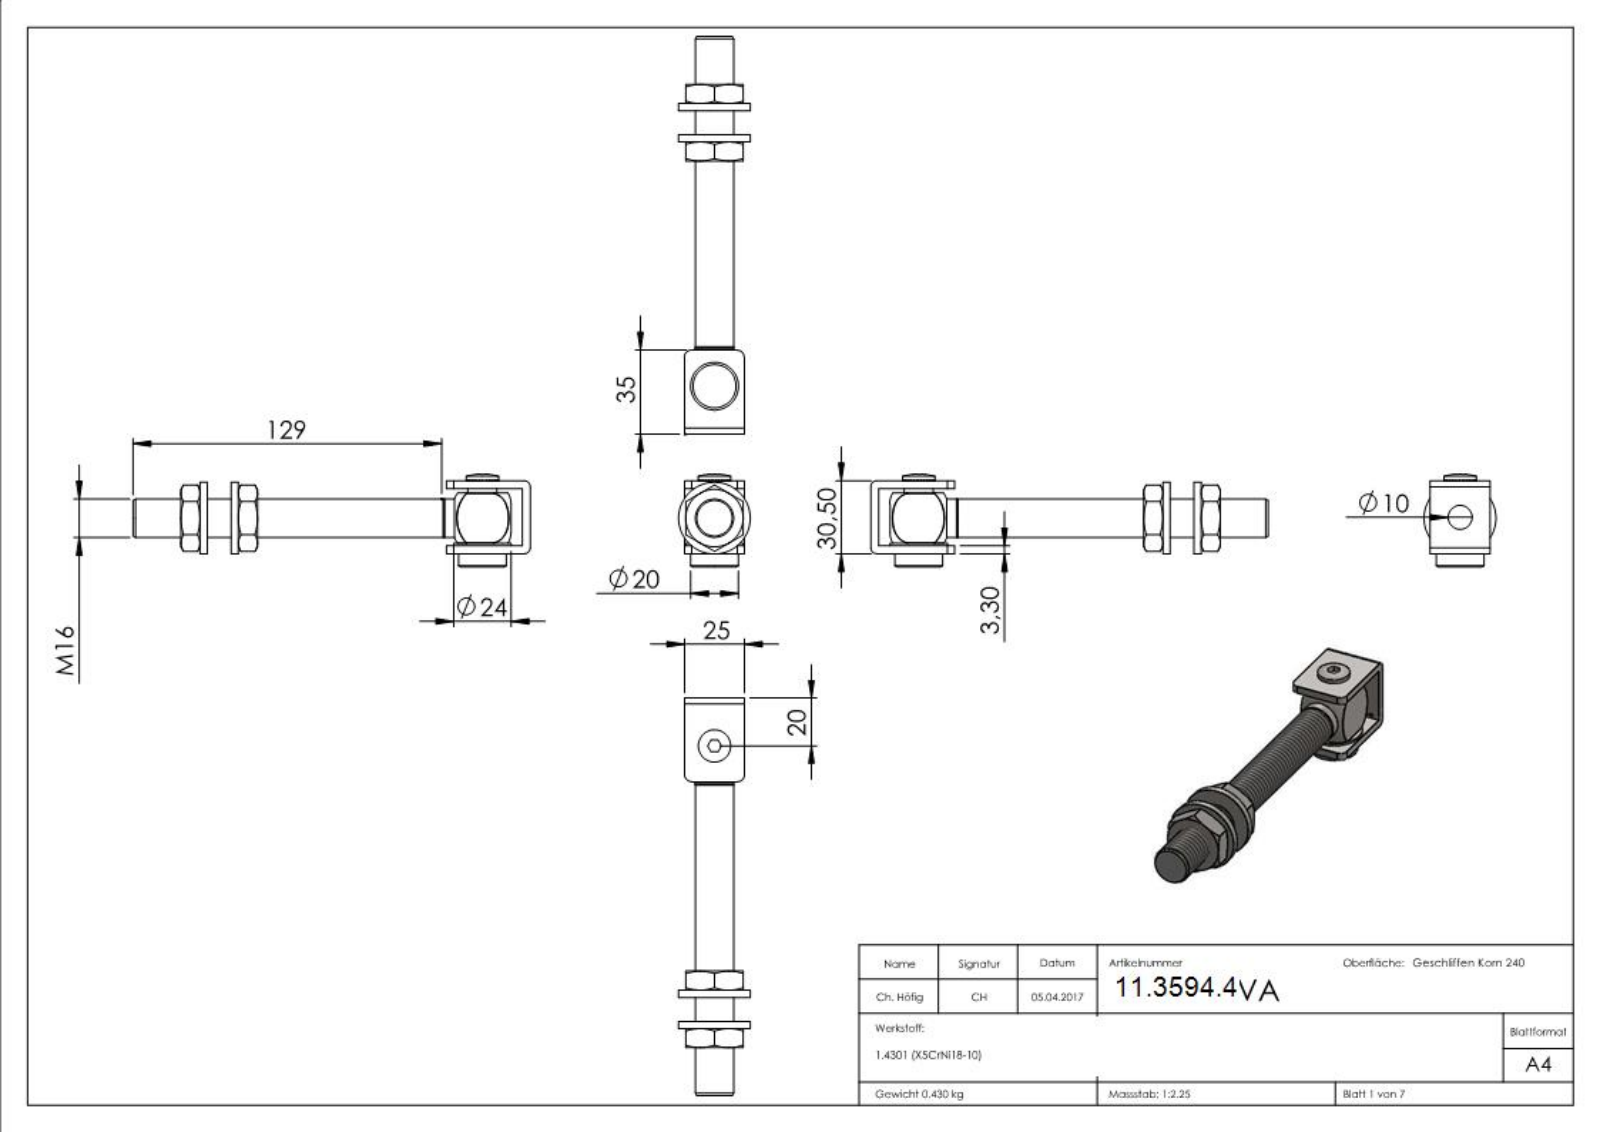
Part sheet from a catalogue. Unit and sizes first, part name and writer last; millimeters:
Units: millimetres
Overall size (bounding box): 170.6 × 39.08 × 35
Round holes (diameter × count): ⌀5 ×1, ⌀6.8 ×1, ⌀10.2 ×1, ⌀12.5 ×1, ⌀12.7 ×1, ⌀14 ×1, ⌀21 ×1
Round bosses / shafts (diameter × count): ⌀35 ×1, ⌀23 ×1, ⌀20 ×1, ⌀16 ×1, ⌀14 ×1, ⌀12.3 ×1, ⌀6 ×1
Partial cylindrical surfaces — rounded edges, fillets, slot ends (radius × count): R1 ×2, R4 ×2, R4.4 ×2, R10.15 ×1
Main face-to-face distances: 3.4, 3, 24, 13, 26.6, 22.5, 16, 21, 10, 8
Hole centre spacings: 0.66
Volume: 56 749 mm³ · Surface area: 25 687 mm²
Bodies: 9 solids, 388 faces (250 planar, 28 cylindrical, 110 other)
Part name (STEP PRODUCT): 130-M16-VA Teil6_normal; 130-M16-VA; 130-M16-VA Teil5; 130-M16-VA Teil3 (+5 more)
STEP written by: SolidWorks 2018 (CONFIG_CONTROL_DESIGN)
